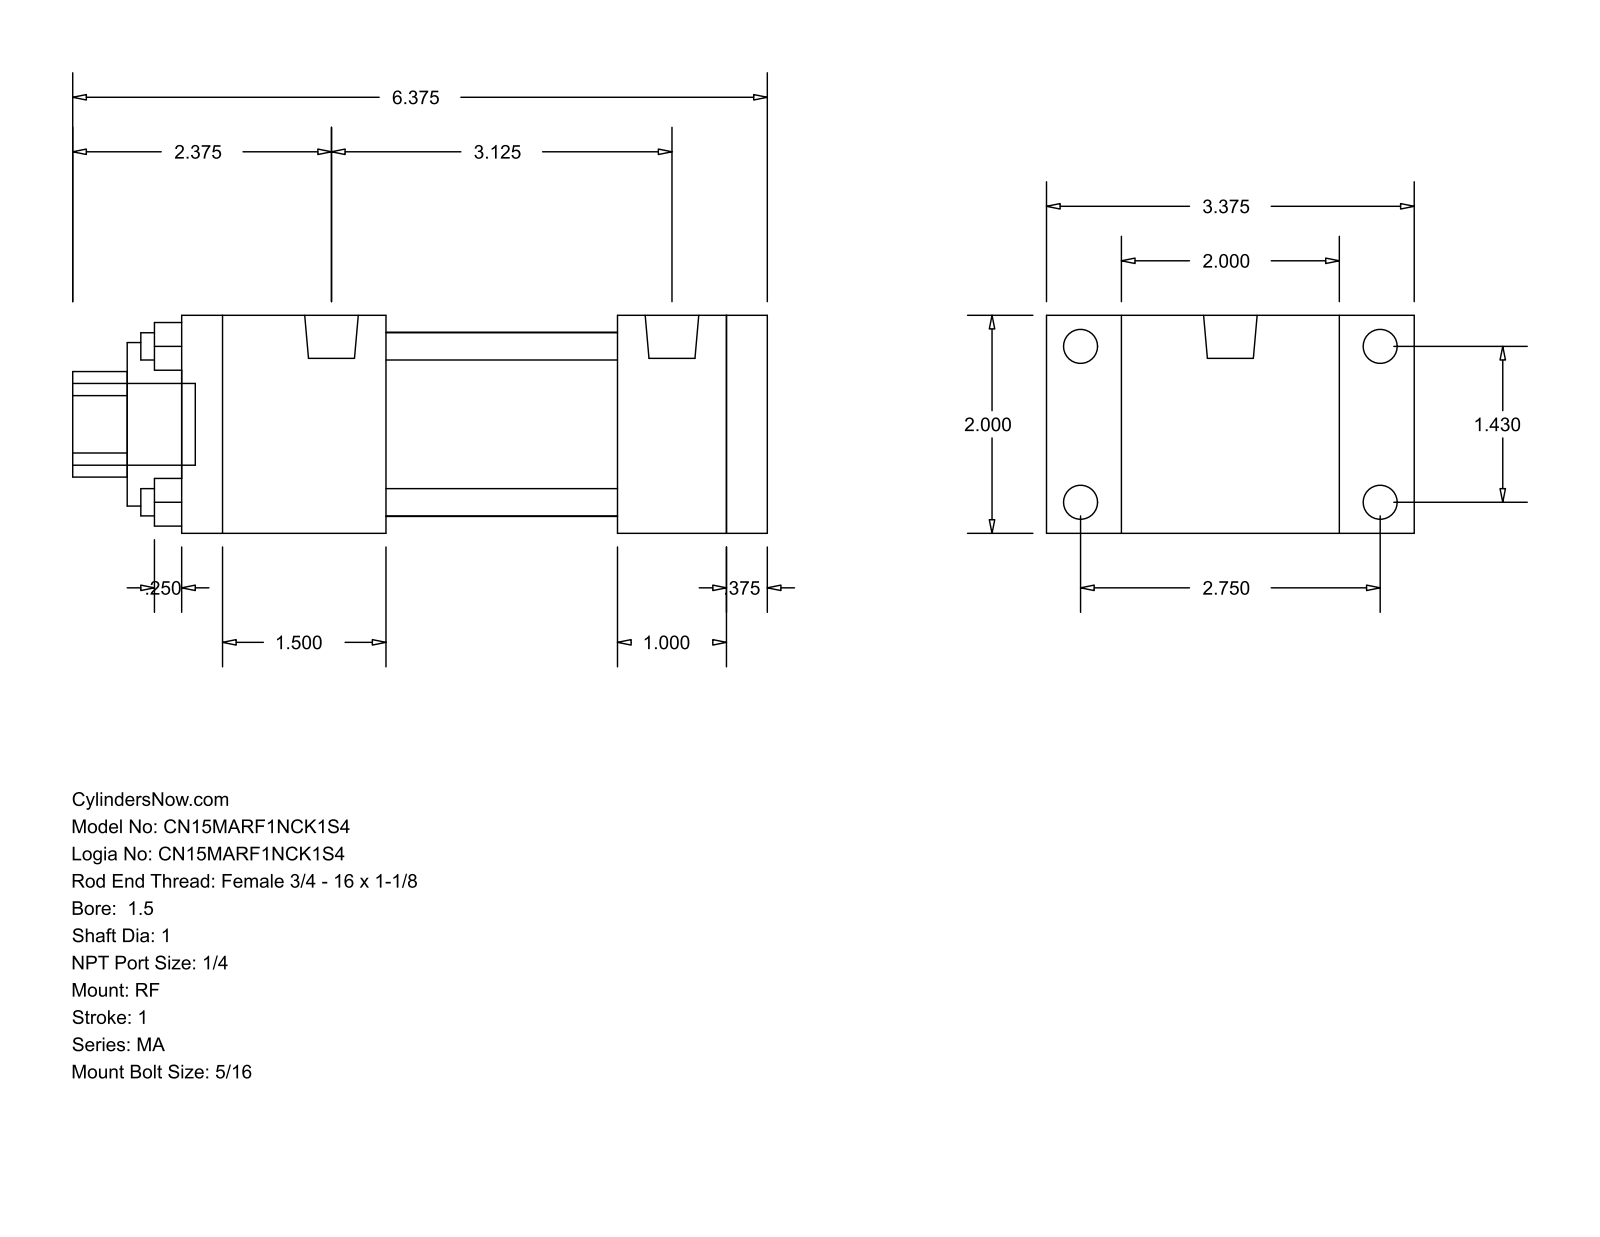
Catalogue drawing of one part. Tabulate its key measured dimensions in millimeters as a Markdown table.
| quantity | value |
| --- | --- |
| part name | MA_RF__0150_1 |
| STEP written by | GSSL Pune (CONFIG_CONTROL_DESIGN) |
| units | millimeters |
| bodies | 0 solids, 92 faces (64 planar, 28 cylindrical, 0 other) |
| overall size | 161.93 × 85.72 × 50.8 |
| round holes (diameter × count) | 6.35 × 4, 25.4 × 1, 38.1 × 1, 42.93 × 1 |
| round bosses / shafts (diameter × count) | 7.94 × 8, 12.49 × 2, 19.05 × 1 |
| partial cylindrical surfaces (radius × count) | 12.29 × 1 |
| main face-to-face distances | 50.8, 9.53, 127, 25.4, 136.53, 101.6, 34.93, 47.63, 53.97, 79.37 |
| hole center spacings | 25.68, 36.32, 51.36 |
